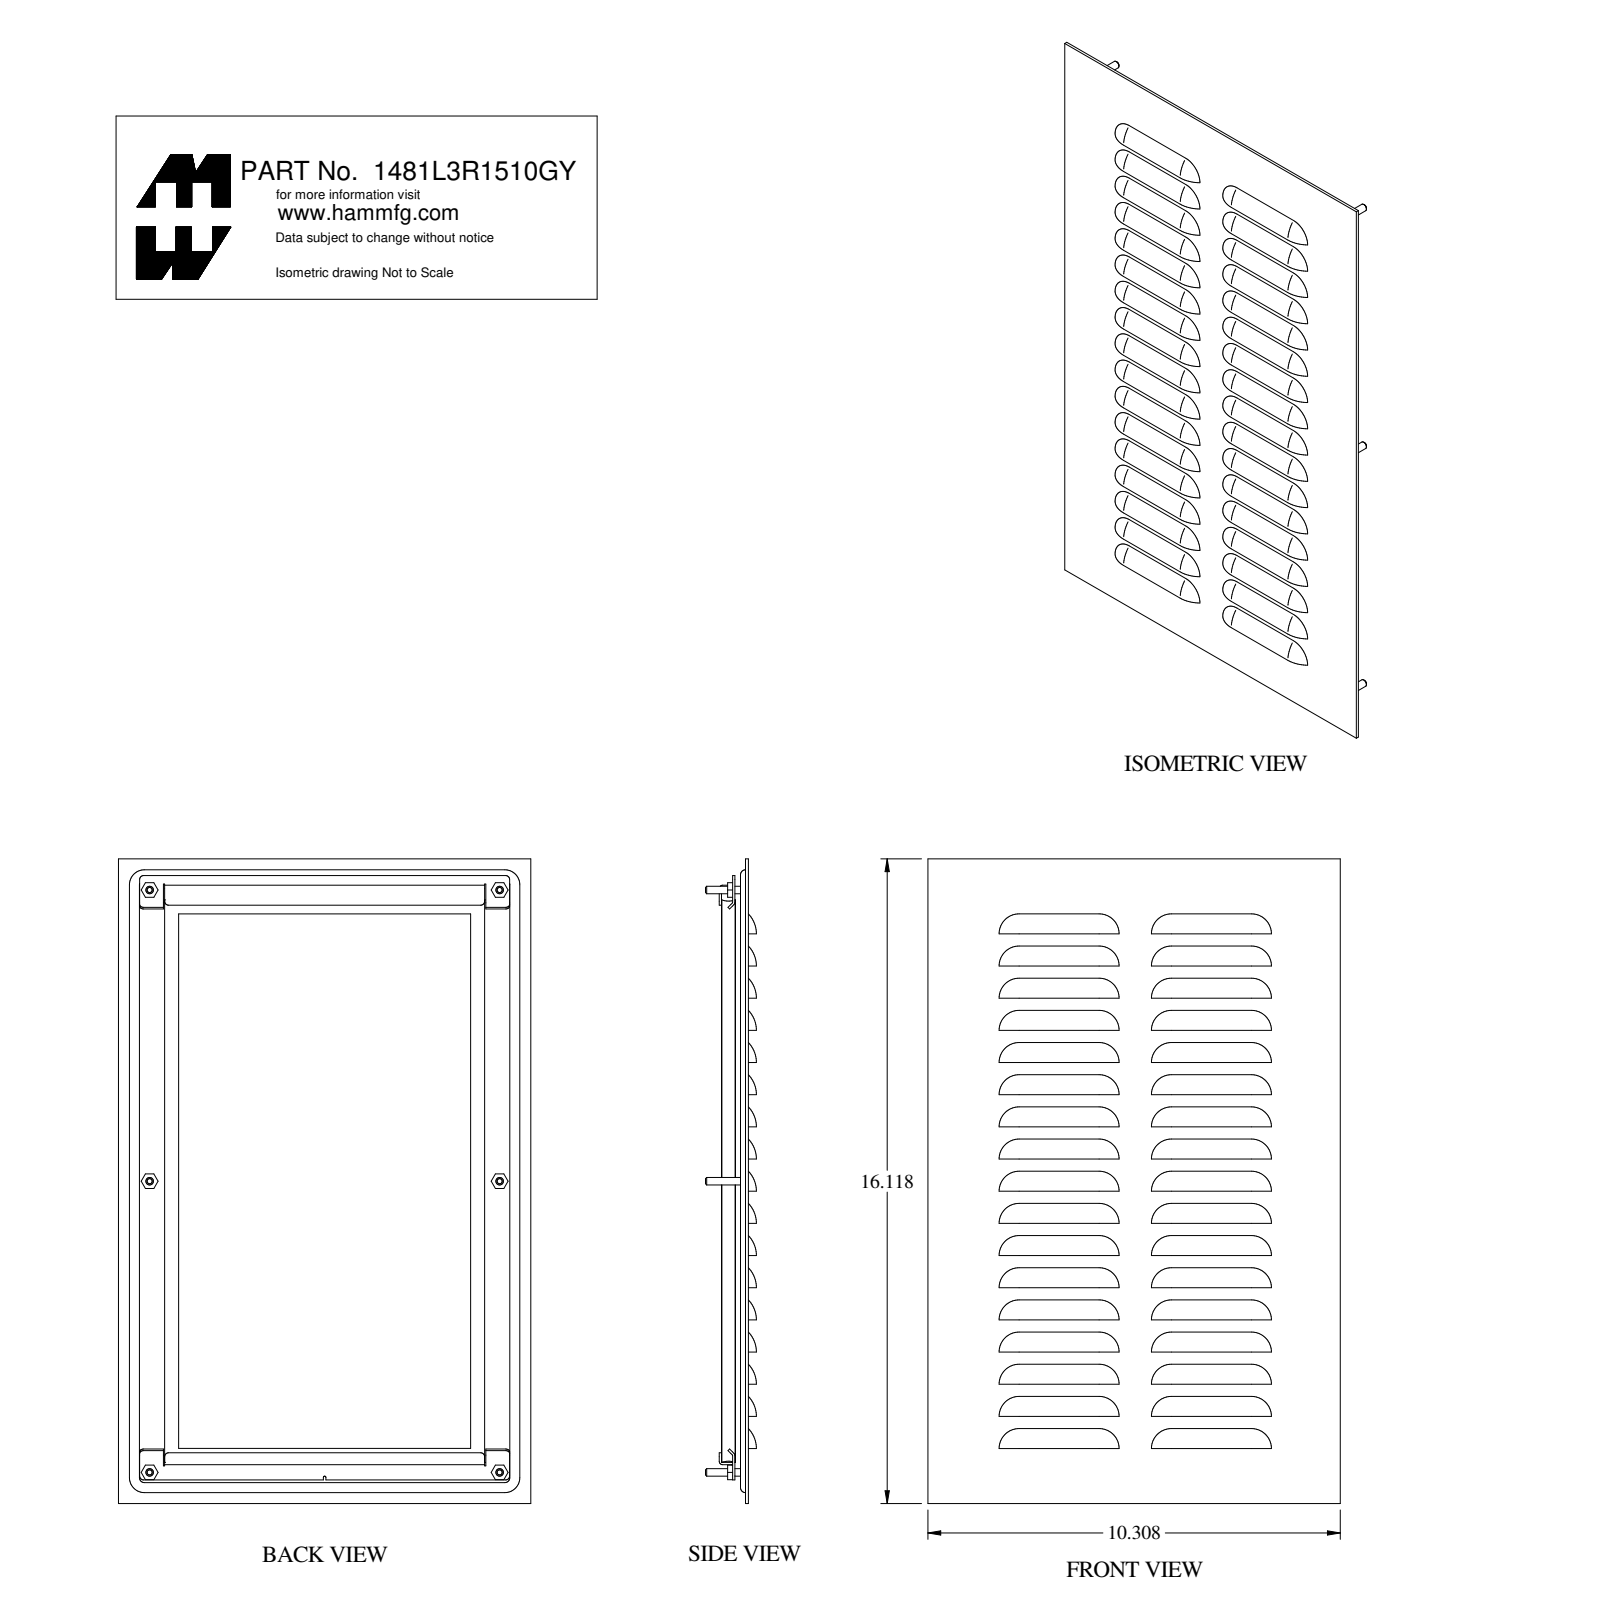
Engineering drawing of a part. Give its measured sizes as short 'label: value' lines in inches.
name: 1481L3R1510GY
written by: SolidWorks 2021 (AUTOMOTIVE_DESIGN)
unit: in
bodies: 17 solids, 544 faces (225 planar, 159 cylindrical, 160 other)
size: 16.118 × 10.308 × 1.272
volume: 44.1 in³; area: 707.7 in²
holes: 6× ⌀0.156, 4× ⌀0.22
bosses: 6× ⌀0.25, 6× ⌀0.188
rounds: 17× R0.653, 17× R0.725, 12× R0.1, 6× R0.029, 6× R0.086, 4× R0.125, 4× R0.126, 4× R0.374
face distances: 0.3, 0.072, 0.25, 0.372, 0.622, 0.55, 0.05, 0.322, 0.672, 0.6
hole spacings: 7.28, 11.382, 14.56, 16.987, 8.75, 8.75
